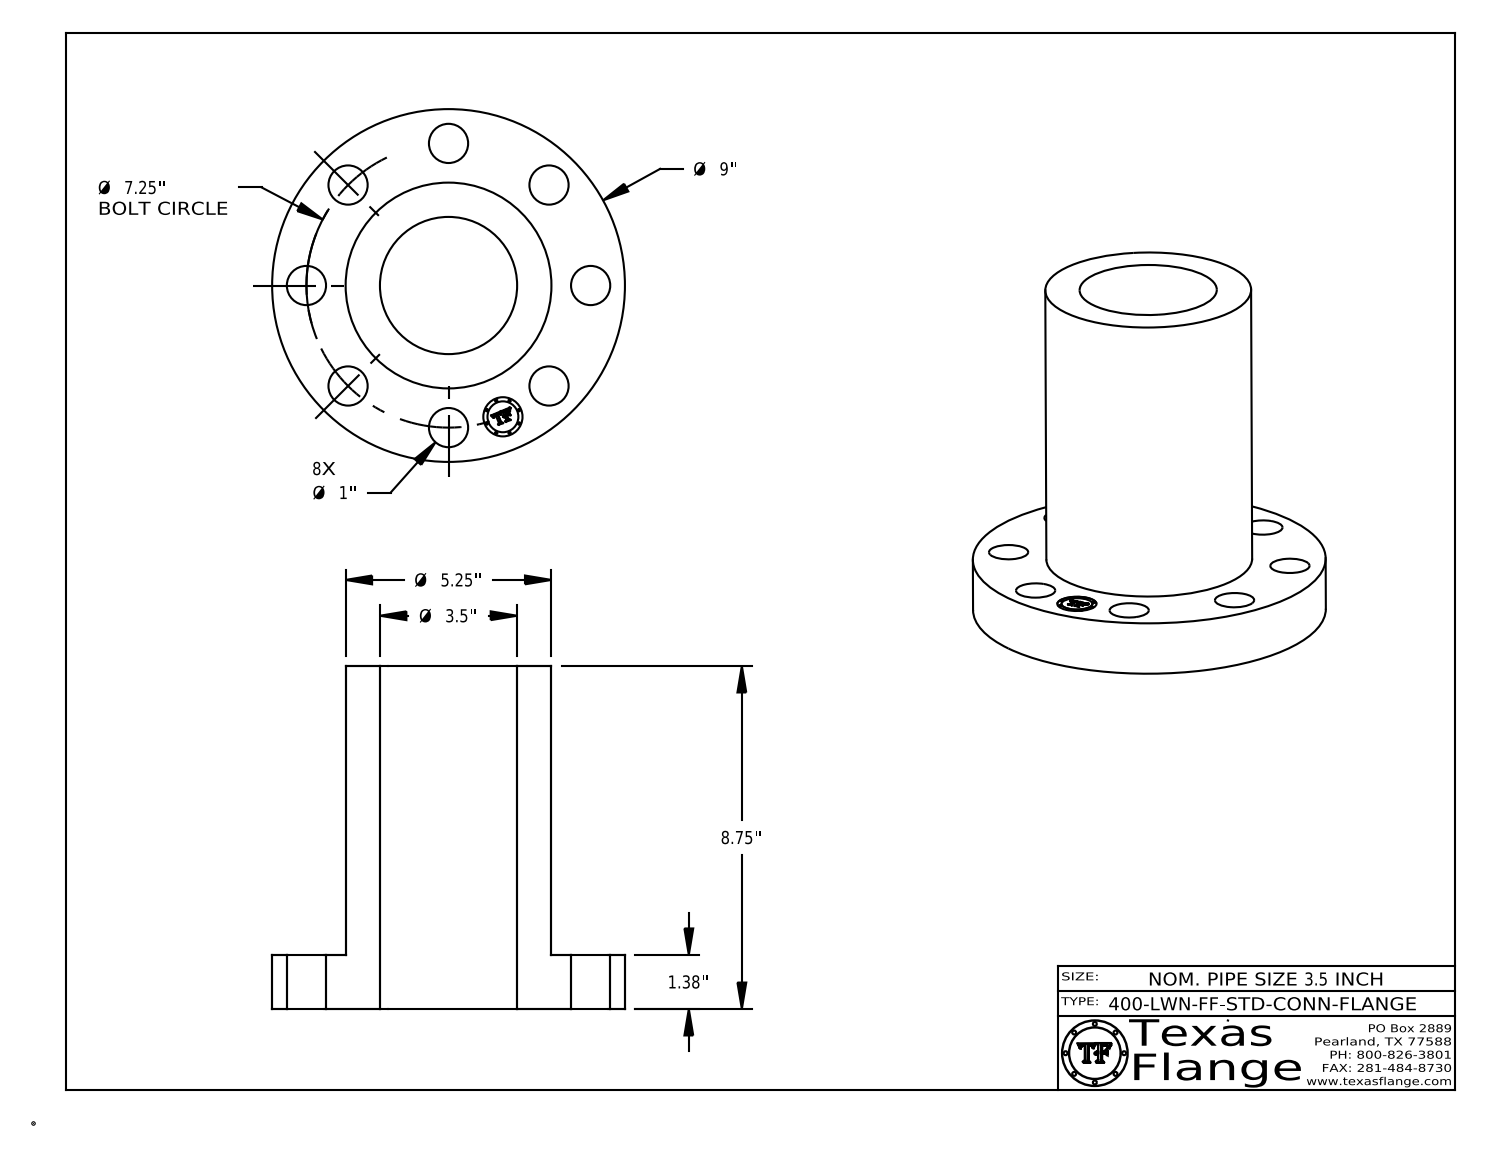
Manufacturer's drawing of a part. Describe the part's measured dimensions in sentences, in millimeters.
The part is named "3.5-400-LWN-FF-STD-CONN-FLANGE". Its 3-D file was written by "CATIA V5 STEP AP214 (AUTOMOTIVE_DESIGN)". It is 1 solid with 410 faces: 368 planar, 42 cylindrical and 0 other. Overall it measures 228.6 by 228.6 by 222.3 millimeters. Its volume is 2 532 000 cubic millimeters and its surface area 249 700 square millimeters. Round holes: 9 of diameter 25.4, 1 of diameter 88.9. Round bosses or shafts: 8 of diameter 1.5, 1 of diameter 228.6, 1 of diameter 133.4, 1 of diameter 20. The main face-to-face distances are 35.1, 222.3, 187.2, 34.9, 187.3, 7.6, 7.4, 1.4, 4.9, 6.3. The hole center spacings are 92.1, 70.5, 130.2, 170.1, 184.2, 35.9, 180.6, 102.3.
